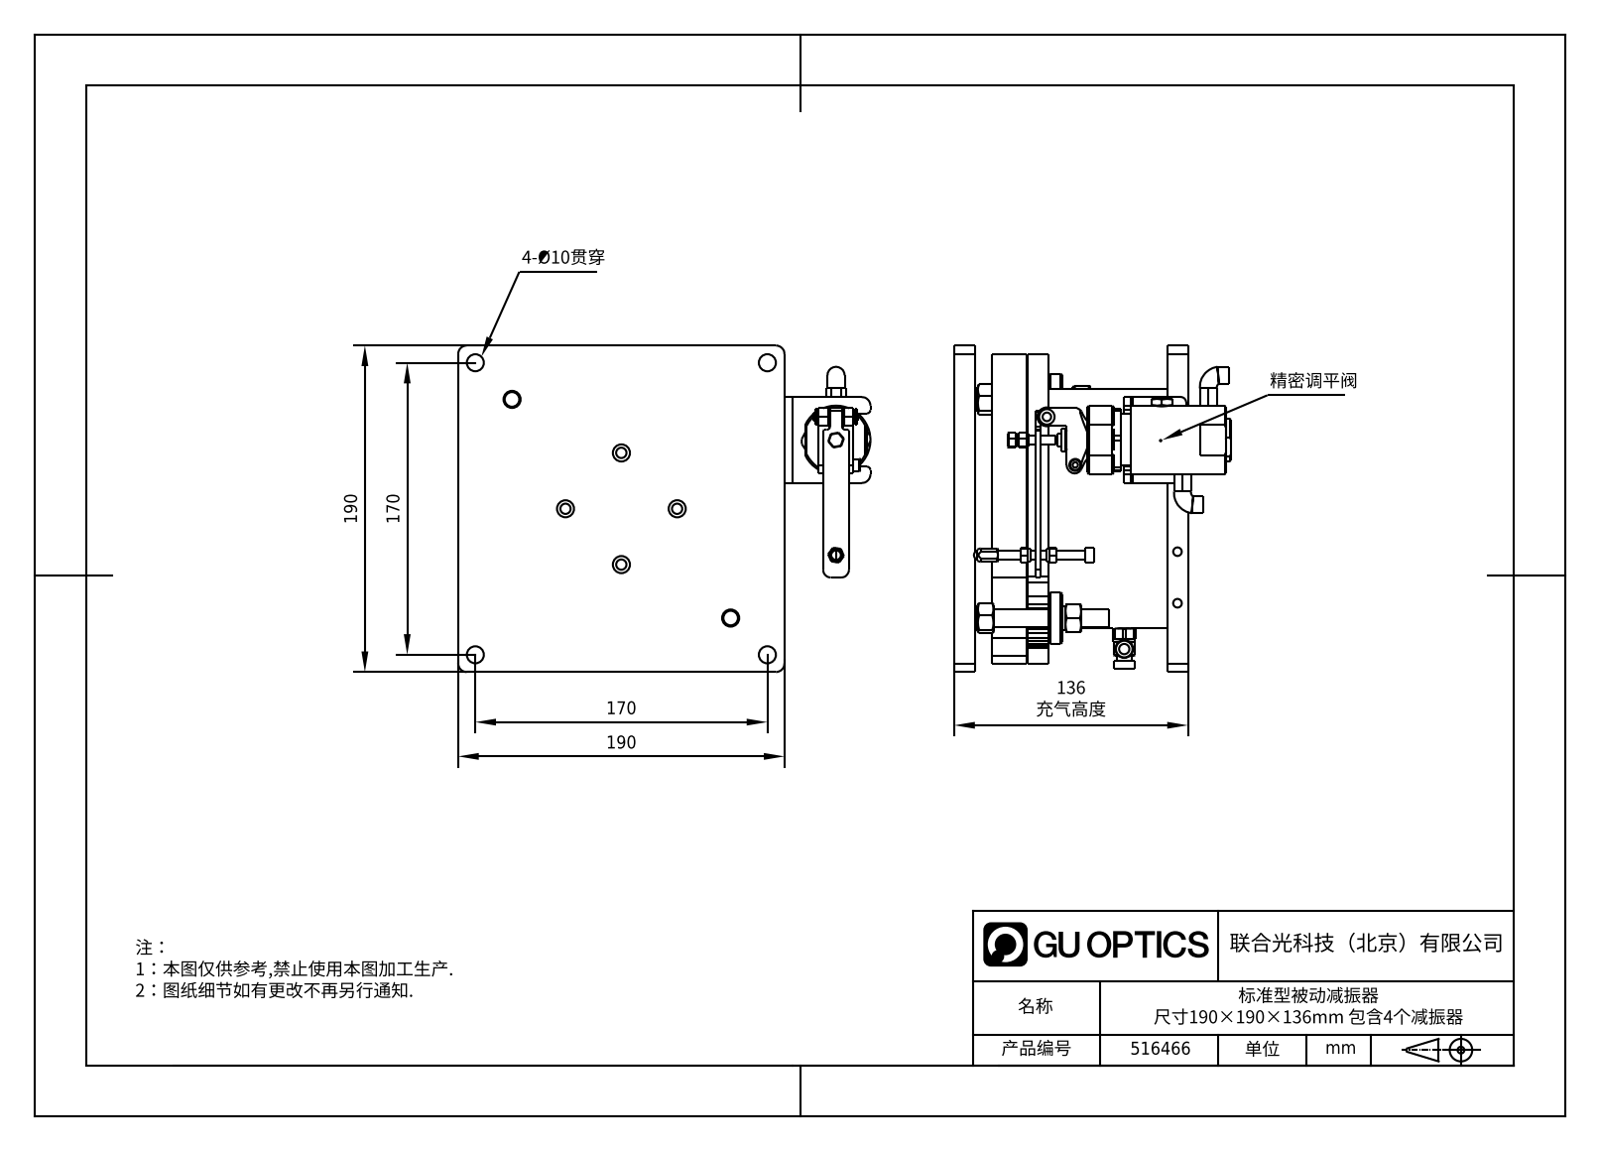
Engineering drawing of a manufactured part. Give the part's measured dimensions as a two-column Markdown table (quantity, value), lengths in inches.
| quantity | value |
| --- | --- |
| part name | 516466 |
| STEP written by | SolidWorks 2020 (CONFIG_CONTROL_DESIGN) |
| units | inches |
| bodies | 0 solids, 422 faces (229 planar, 148 cylindrical, 45 other) |
| overall size | 9.449 × 7.48 × 6.339 |
| round holes (diameter × count) | 0.197 × 5, 0.394 × 4, 0.453 × 4, 0.276 × 2, 0.382 × 1, 0.512 × 1, 1.575 × 1 |
| round bosses / shafts (diameter × count) | 0.394 × 8, 0.165 × 6, 1.181 × 3, 0.315 × 3, 0.539 × 2, 0.276 × 2, 0.197 × 2, 5.484 × 1 |
| partial cylindrical surfaces (radius × count) | 0.197 × 10, 0.394 × 10, 0.079 × 8, 0.012 × 5, 0.787 × 4, 0.118 × 2, 0.177 × 2, 2.874 × 2 |
| main face-to-face distances | 0.472, 4.882, 5.354, 4.409, 3.189, 1.693, 2.165, 0.827, 2.717, 1.299 |
| hole center spacings | 5.912, 6.693, 1.181, 1.189, 3.15, 8.276, 9.465, 1.609 |
